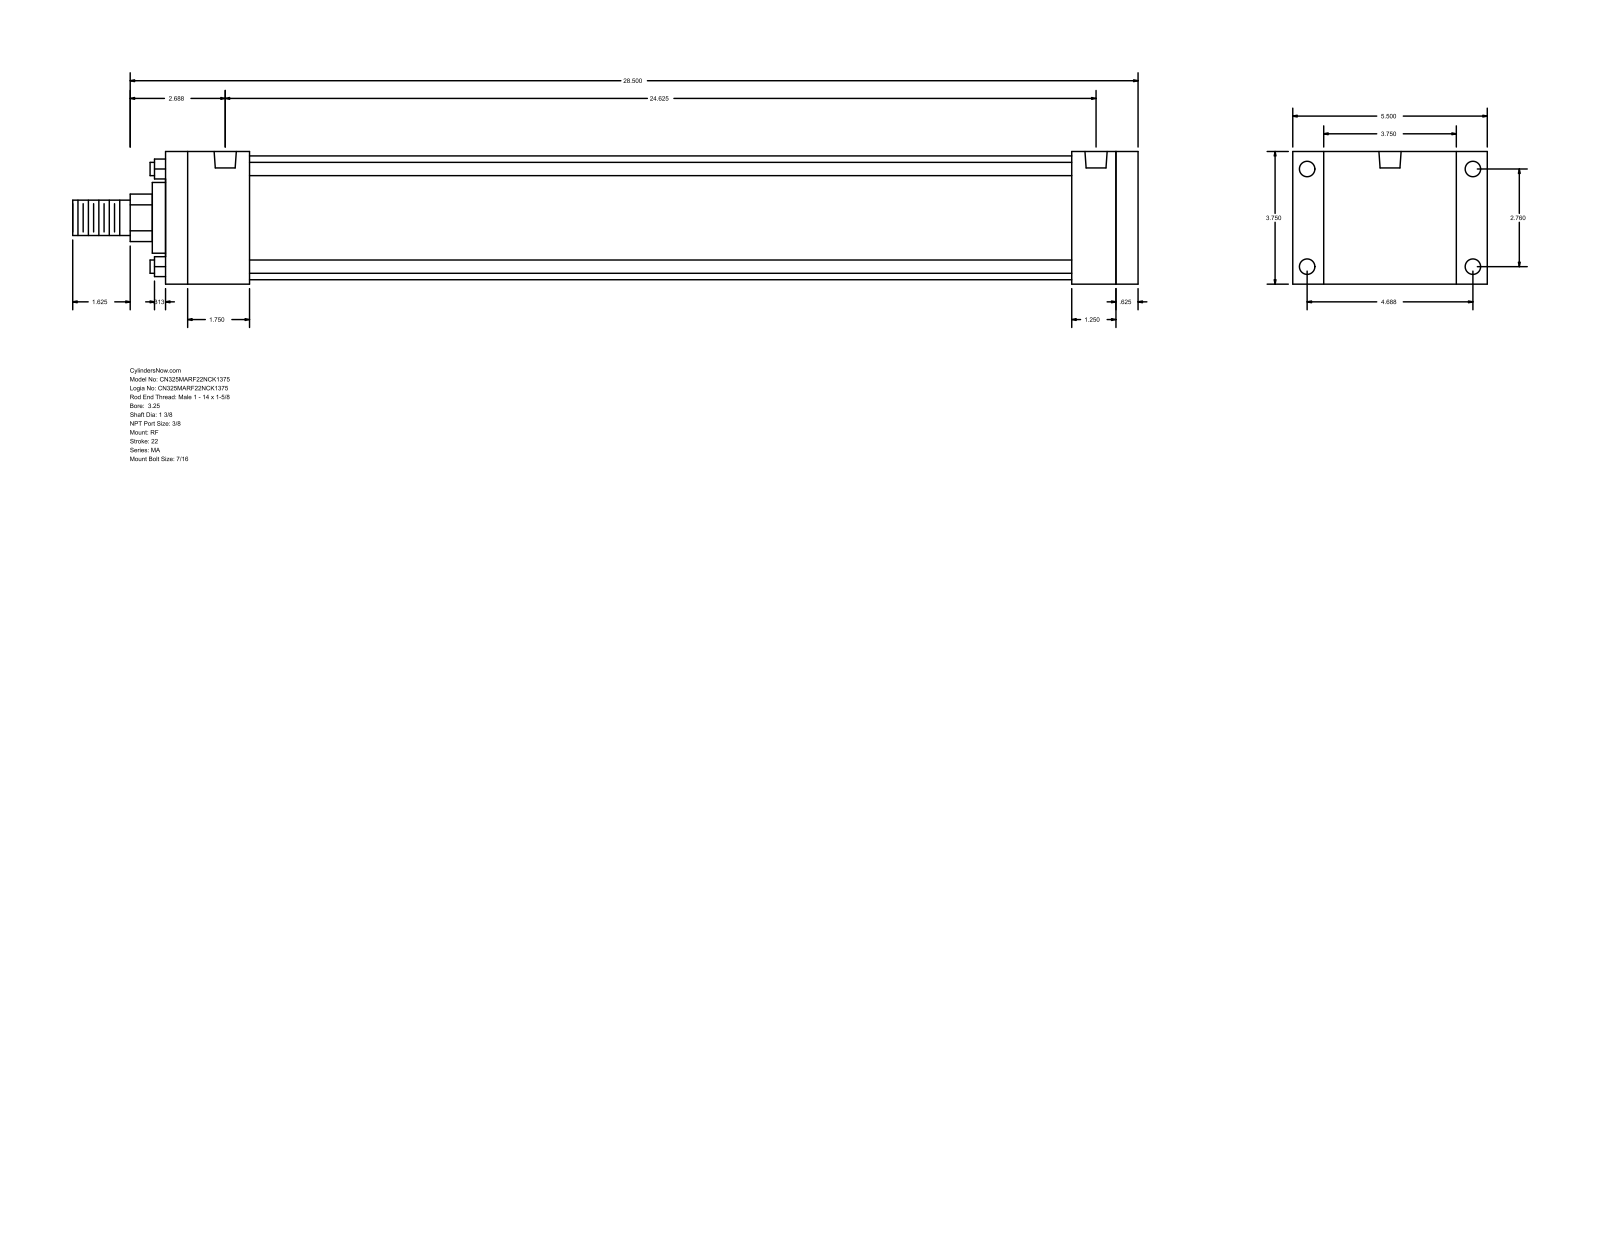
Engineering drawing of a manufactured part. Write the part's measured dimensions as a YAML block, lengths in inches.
part_name: "MA_RF__0325_1.375"
step_written_by: "GSSL Pune (CONFIG_CONTROL_DESIGN)"
units: inches
bodies: {solids: 0, faces: 92, planar: 64, cylindrical: 28, other: 0}
overall_size: [30.125, 5.5, 3.75]
round_holes:
  - {diameter: 0.437, count: 8}
  - {diameter: 0.627, count: 2}
round_bosses_or_shafts:
  - {diameter: 0.375, count: 4}
  - {diameter: 3.5, count: 1}
  - {diameter: 2, count: 1}
  - {diameter: 1.375, count: 1}
  - {diameter: 1, count: 1}
partial_cylinders:
  - {radius: 0.672, count: 1}
face_to_face_distances: [3.75, 27.5, 0.625, 26.875, 0.875, 4.625, 25.625, 1.25, 1.875, 2.375]
hole_center_spacings: [2.76, 4.687, 5.439, 24.25, 0.187, 0.188, 24.437, 24.438]
